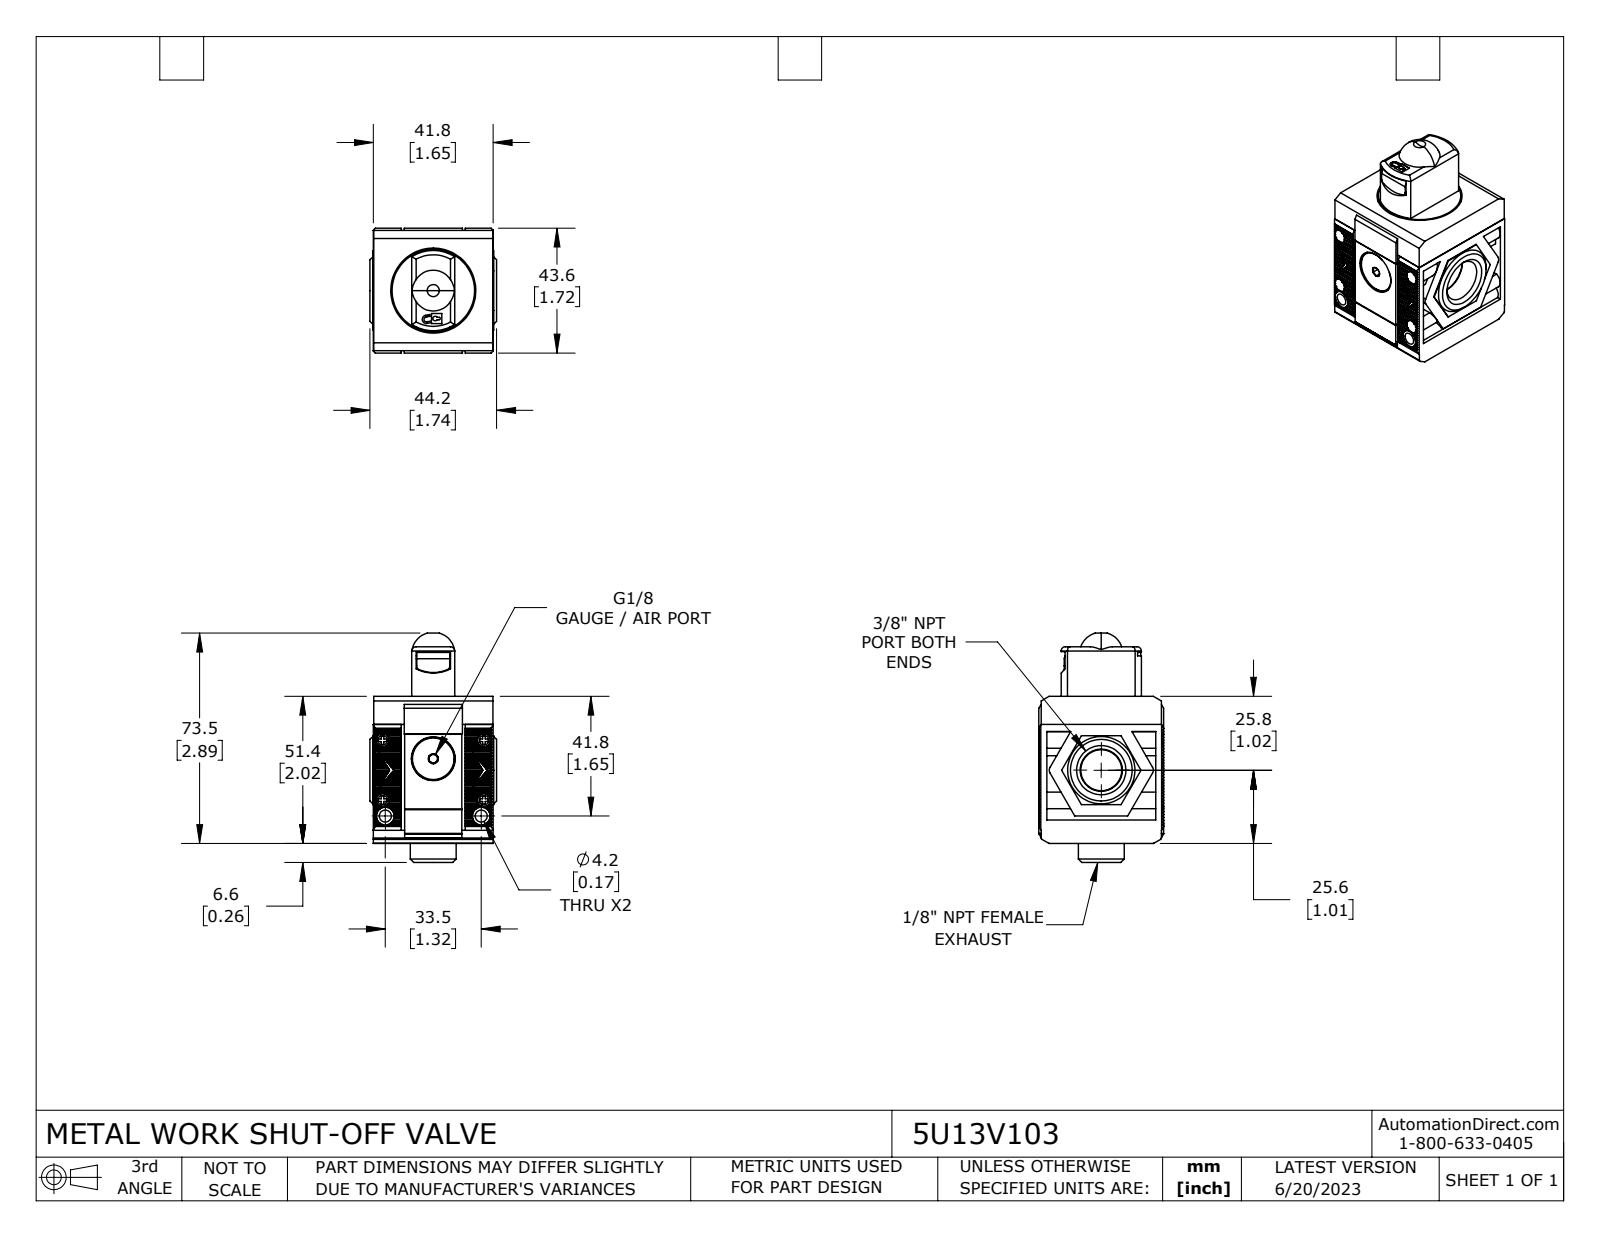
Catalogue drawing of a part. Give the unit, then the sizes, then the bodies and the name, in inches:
Units: inches
Overall size (bounding box): 3.152 × 1.74 × 1.717
Round holes (diameter × count): ⌀0.083 ×4, ⌀0.118 ×4, ⌀0.185 ×4, ⌀0.165 ×2, ⌀0.337 ×2, ⌀0.602 ×1, ⌀1.169 ×1, ⌀1.232 ×1
Round bosses / shafts (diameter × count): ⌀0.181 ×4, ⌀0.102 ×4, ⌀0.244 ×2, ⌀1.26 ×1, ⌀1.134 ×1, ⌀0.898 ×1, ⌀0.717 ×1, ⌀0.63 ×1
Partial cylindrical surfaces — rounded edges, fillets, slot ends (radius × count): R0.024 ×4, R0.059 ×4, R0.122 ×4, R0.008 ×2, R0.079 ×2, R0.018 ×1, R0.033 ×1, R0.039 ×1
Main face-to-face distances: 1.638, 1.642, 1.339, 1.673, 0.307, 0.386, 2.024, 0.11, 0.043, 0.031
Hole centre spacings: 0.222, 0.742, 0.823, 0.9, 1.027, 1.042, 1.374, 1.394
Volume: 5.753 in³ · Surface area: 53.37 in²
Bodies: 13 solids, 1155 faces (817 planar, 206 cylindrical, 132 other)
Part name (STEP PRODUCT): 5U13V103
STEP written by: SolidWorks 2021 (CONFIG_CONTROL_DESIGN)
